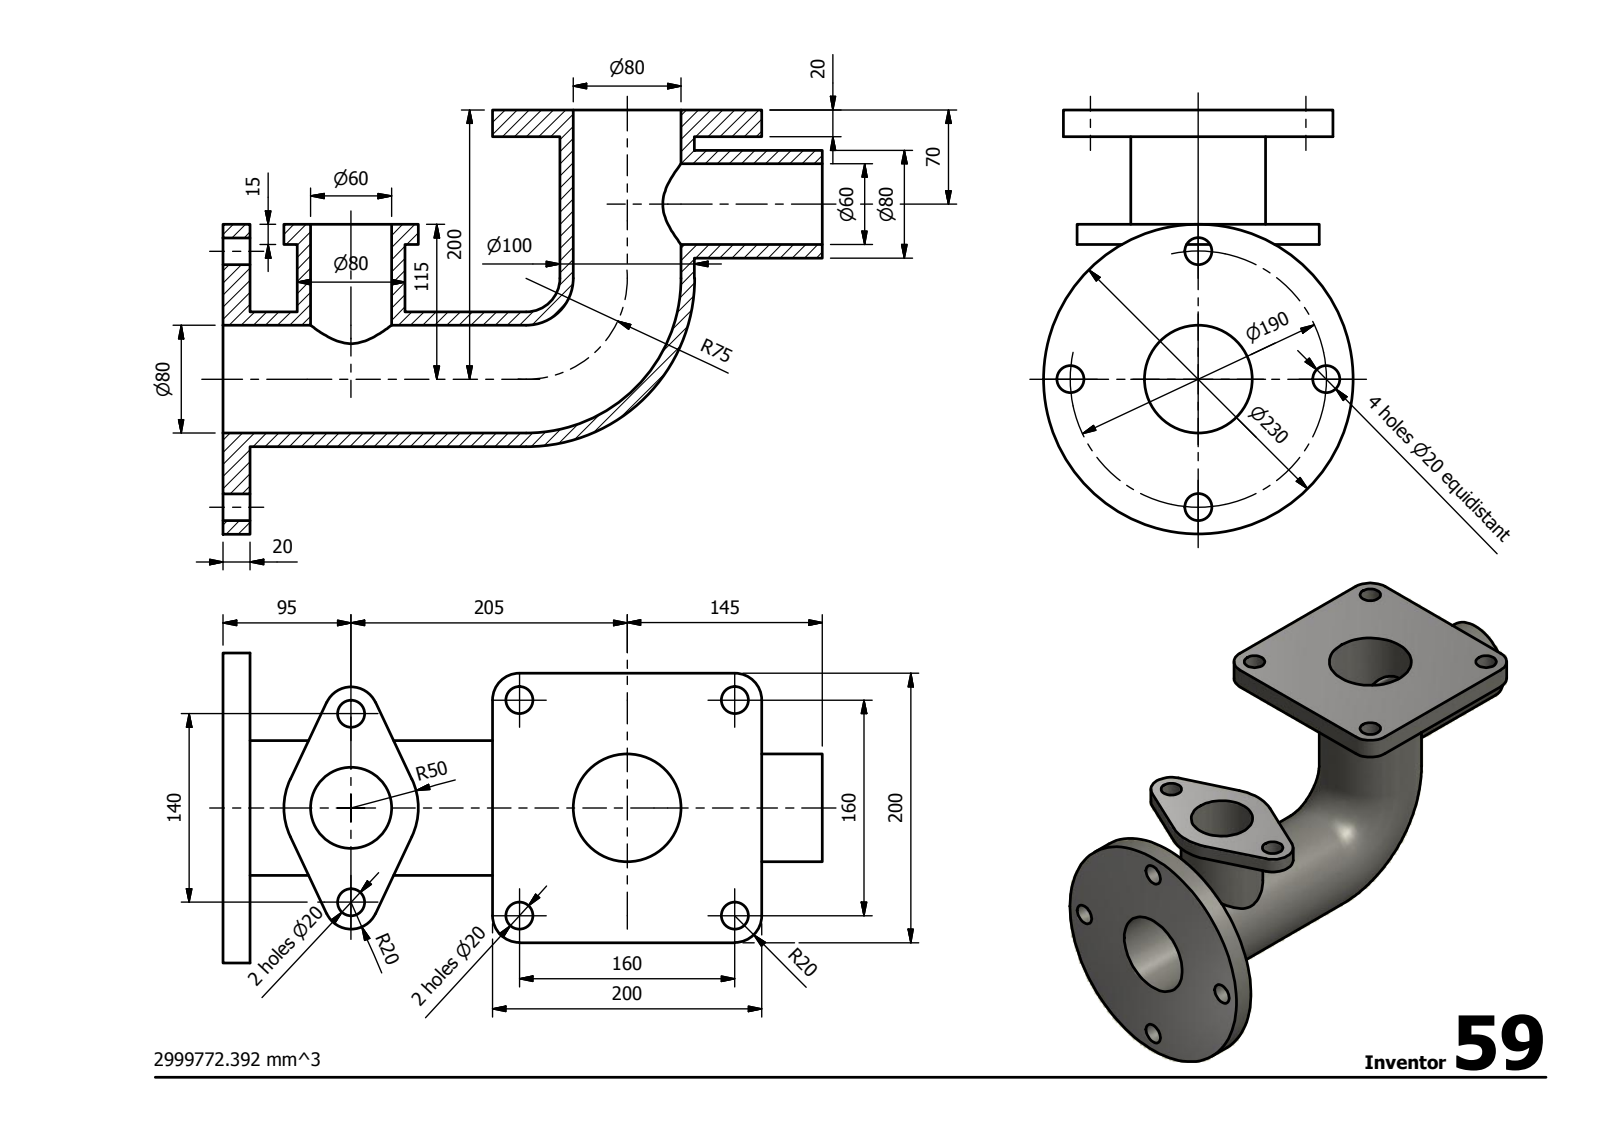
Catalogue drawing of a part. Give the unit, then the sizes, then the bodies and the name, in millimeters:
Units: millimetres
Overall size (bounding box): 445 × 315 × 230
Round holes (diameter × count): ⌀20 ×10, ⌀60 ×2, ⌀80 ×2
Round bosses / shafts (diameter × count): ⌀100 ×2, ⌀80 ×2, ⌀230 ×1
Partial cylindrical surfaces — rounded edges, fillets, slot ends (radius × count): R20 ×6, R50 ×1
Main face-to-face distances: 20, 200, 65, 85, 15, 80, 100, 400, 180, 380
Hole centre spacings: 95, 113.14, 134.35, 160, 70, 125.4, 148.41, 161.01
Volume: 3 000 000 mm³ · Surface area: 508 975 mm²
Bodies: 1 solid, 44 faces (15 planar, 27 cylindrical, 2 other)
STEP written by: Autodesk Inventor 2014 (AUTOMOTIVE_DESIGN)
